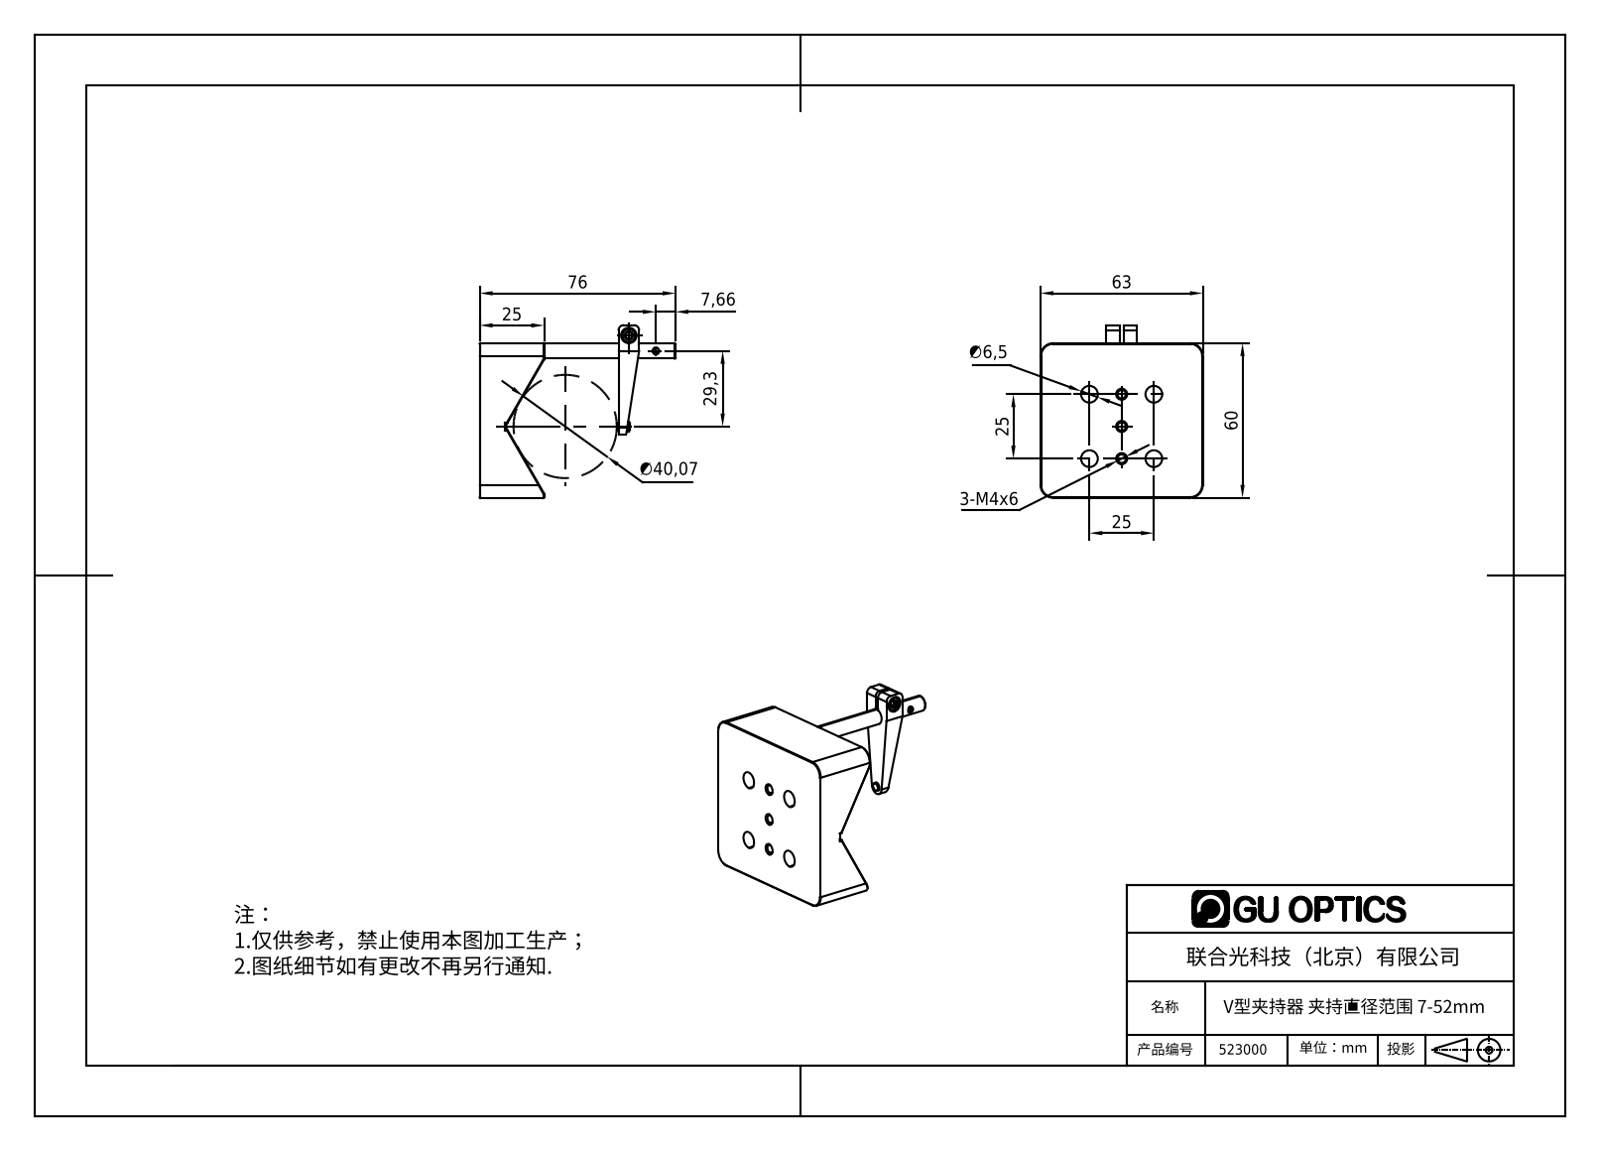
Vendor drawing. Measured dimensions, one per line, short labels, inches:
name: 1.3.5.2_ZZV-63_中型V形安装座，长度63mm，附带压臂，A
written by: SolidWorks 2018 (AUTOMOTIVE_DESIGN)
unit: in
bodies: 0 solids, 146 faces (55 planar, 51 cylindrical, 40 other)
size: 2.992 × 2.638 × 2.48
holes: 6× ⌀0.13, 4× ⌀0.256, 4× ⌀0.413, 1× ⌀0.091, 1× ⌀0.11, 1× ⌀0.236
bosses: 1× ⌀0.236, 1× ⌀0.157, 1× ⌀0.118
rounds: 4× R0.197, 2× R0.079, 1× R0.118
face distances: 2.362, 2.48, 0.984, 2.121, 1.137, 0.382, 0.602, 1.739, 1.004, 1.476
hole spacings: 0.492, 0.984, 0.696, 1.1, 0.702, 0.728, 0.824, 0.984
